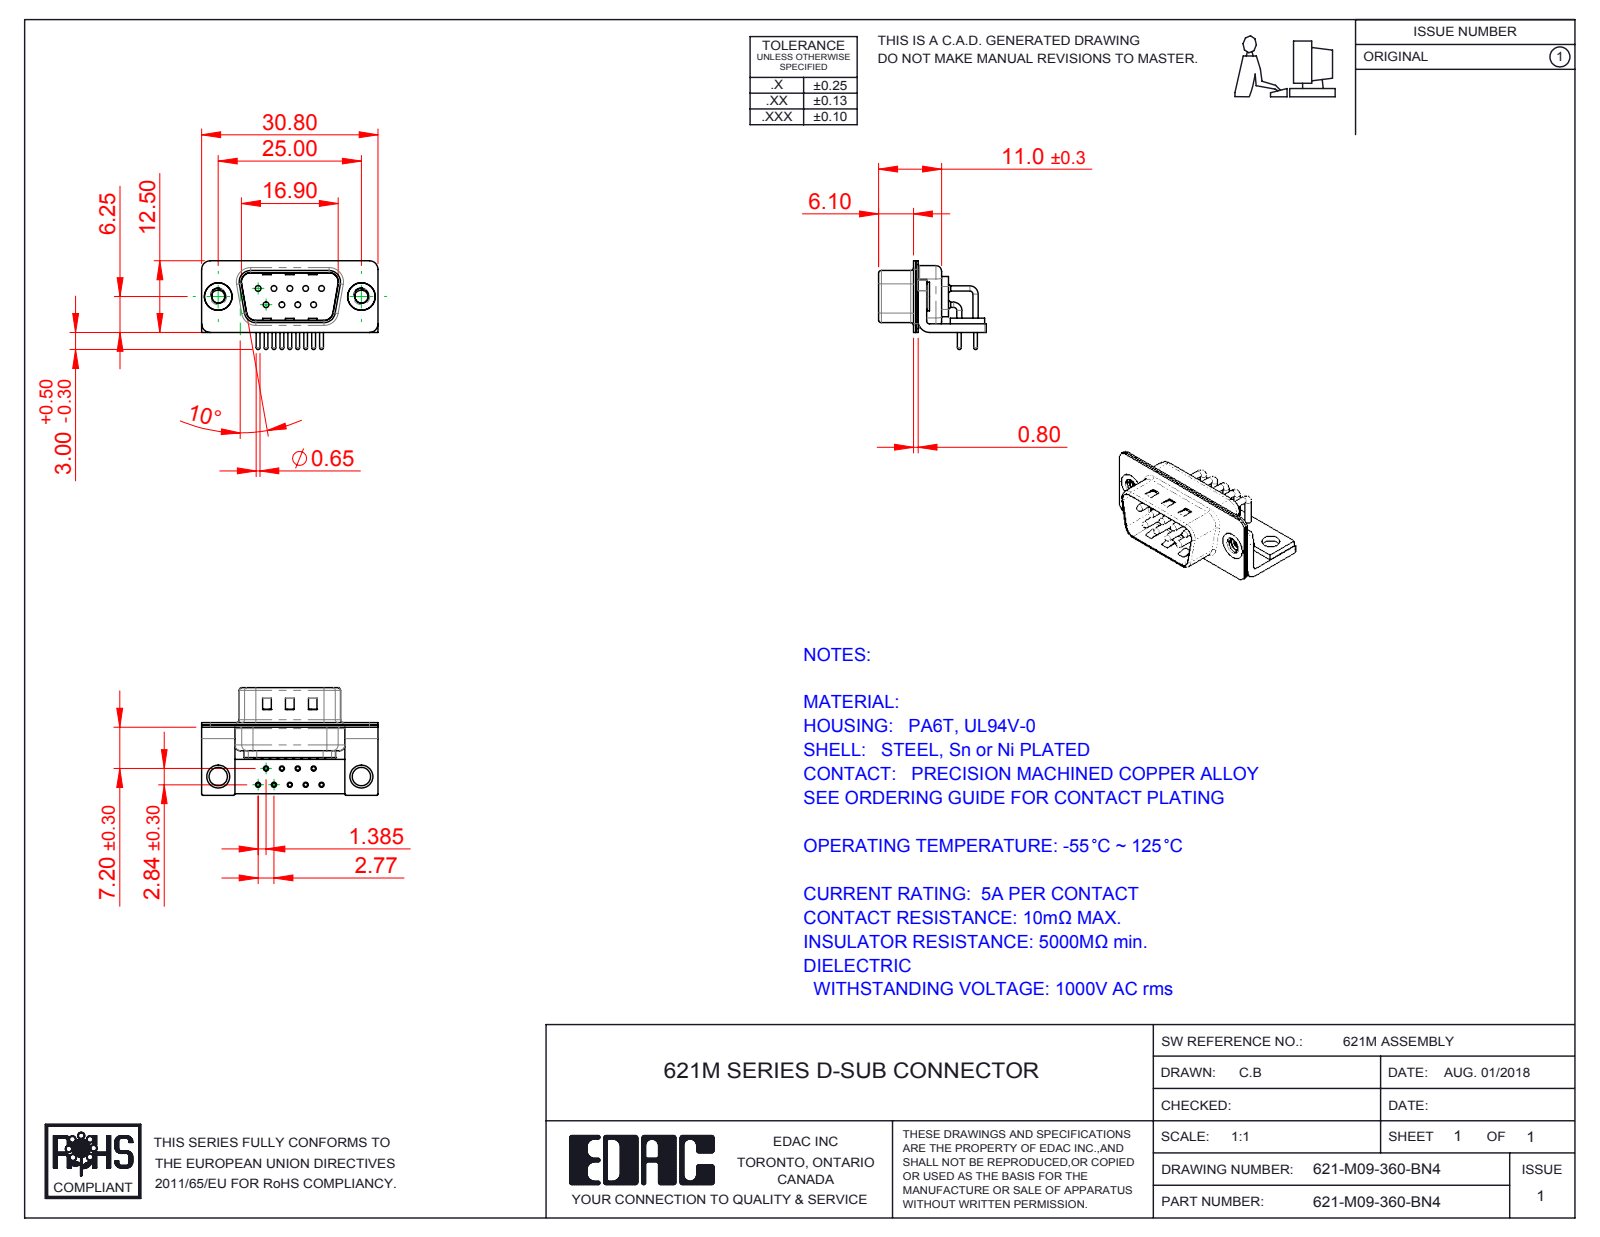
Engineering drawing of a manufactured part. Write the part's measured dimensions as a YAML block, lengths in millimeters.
part_name: "621M Shell Front_09 Contacts; 621M Shell Rear_09 Contacts; 621M Contact Row 2; 621M Housing_09 Contacts (+5 more)"
step_written_by: "SolidWorks 2016 (CONFIG_CONTROL_DESIGN)"
units: millimeters
bodies: {solids: 17, faces: 1362, planar: 709, cylindrical: 493, other: 160}
overall_size: [30.8, 18.8, 15.49]
volume: 1755
surface_area: 4812
round_holes:
  - {diameter: 0.9, count: 9}
  - {diameter: 1, count: 9}
  - {diameter: 1.7, count: 9}
  - {diameter: 2, count: 9}
  - {diameter: 2.26, count: 2}
  - {diameter: 3.2, count: 2}
  - {diameter: 4, count: 2}
  - {diameter: 4.8, count: 2}
round_bosses_or_shafts:
  - {diameter: 1.5, count: 9}
  - {diameter: 0.9, count: 9}
  - {diameter: 0.65, count: 9}
  - {diameter: 5, count: 2}
  - {diameter: 4.9, count: 2}
partial_cylinders:
  - {radius: 0.25, count: 16}
  - {radius: 1.5, count: 16}
  - {radius: 2, count: 13}
  - {radius: 0.5, count: 9}
  - {radius: 1.01, count: 9}
  - {radius: 1.6, count: 8}
  - {radius: 0.6, count: 4}
  - {radius: 0.65, count: 4}
face_to_face_distances: [0.4, 1.5, 0.8, 0.85, 1.25, 1, 10.4, 9.55, 1.9, 2.5]
hole_center_spacings: [3.16, 2.77, 5.54, 5.03, 5.04, 8.31, 7.48, 7.49]
